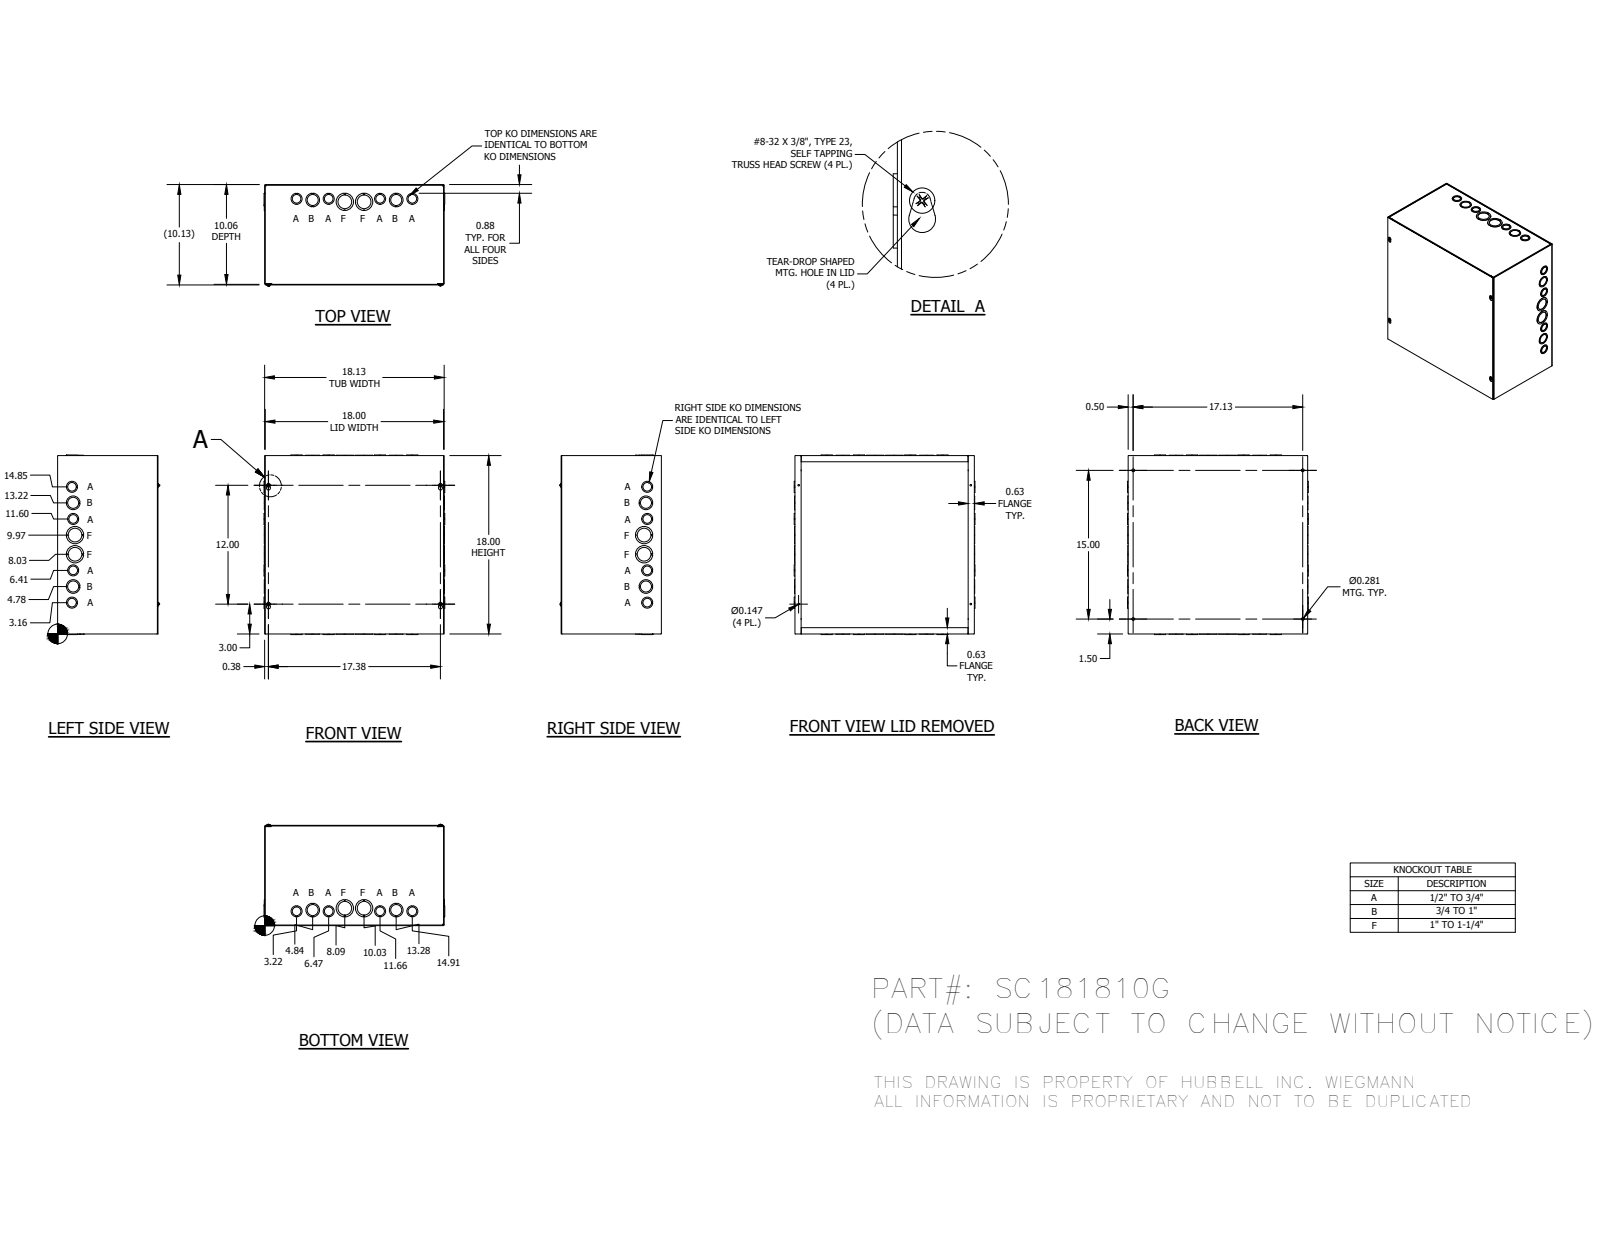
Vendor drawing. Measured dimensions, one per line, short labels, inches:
name: SC181810GBLR; SC1810GTB; SC1818GLPA; 34056 (+1 more)
written by: Autodesk Inventor 2014 (AUTOMOTIVE_DESIGN)
unit: in
bodies: 37 solids, 1167 faces (859 planar, 240 cylindrical, 68 other)
size: 18.25 × 18.125 × 10.225
holes: 14× ⌀1.125, 10× ⌀0.875, 8× ⌀1.375, 4× ⌀0.147, 4× ⌀0.281, 4× ⌀1.75
bosses: 4× ⌀0.384, 4× ⌀0.164
rounds: 12× R0.016, 12× R0.078, 4× R0.125, 4× R0.203
face distances: 0.063, 10.063, 18, 10, 17.937, 18.063, 10.125, 17.875, 18.125, 0.125
hole spacings: 1.505, 1.63, 1.63, 1.655, 3.25, 3.256, 3.579, 4.885
